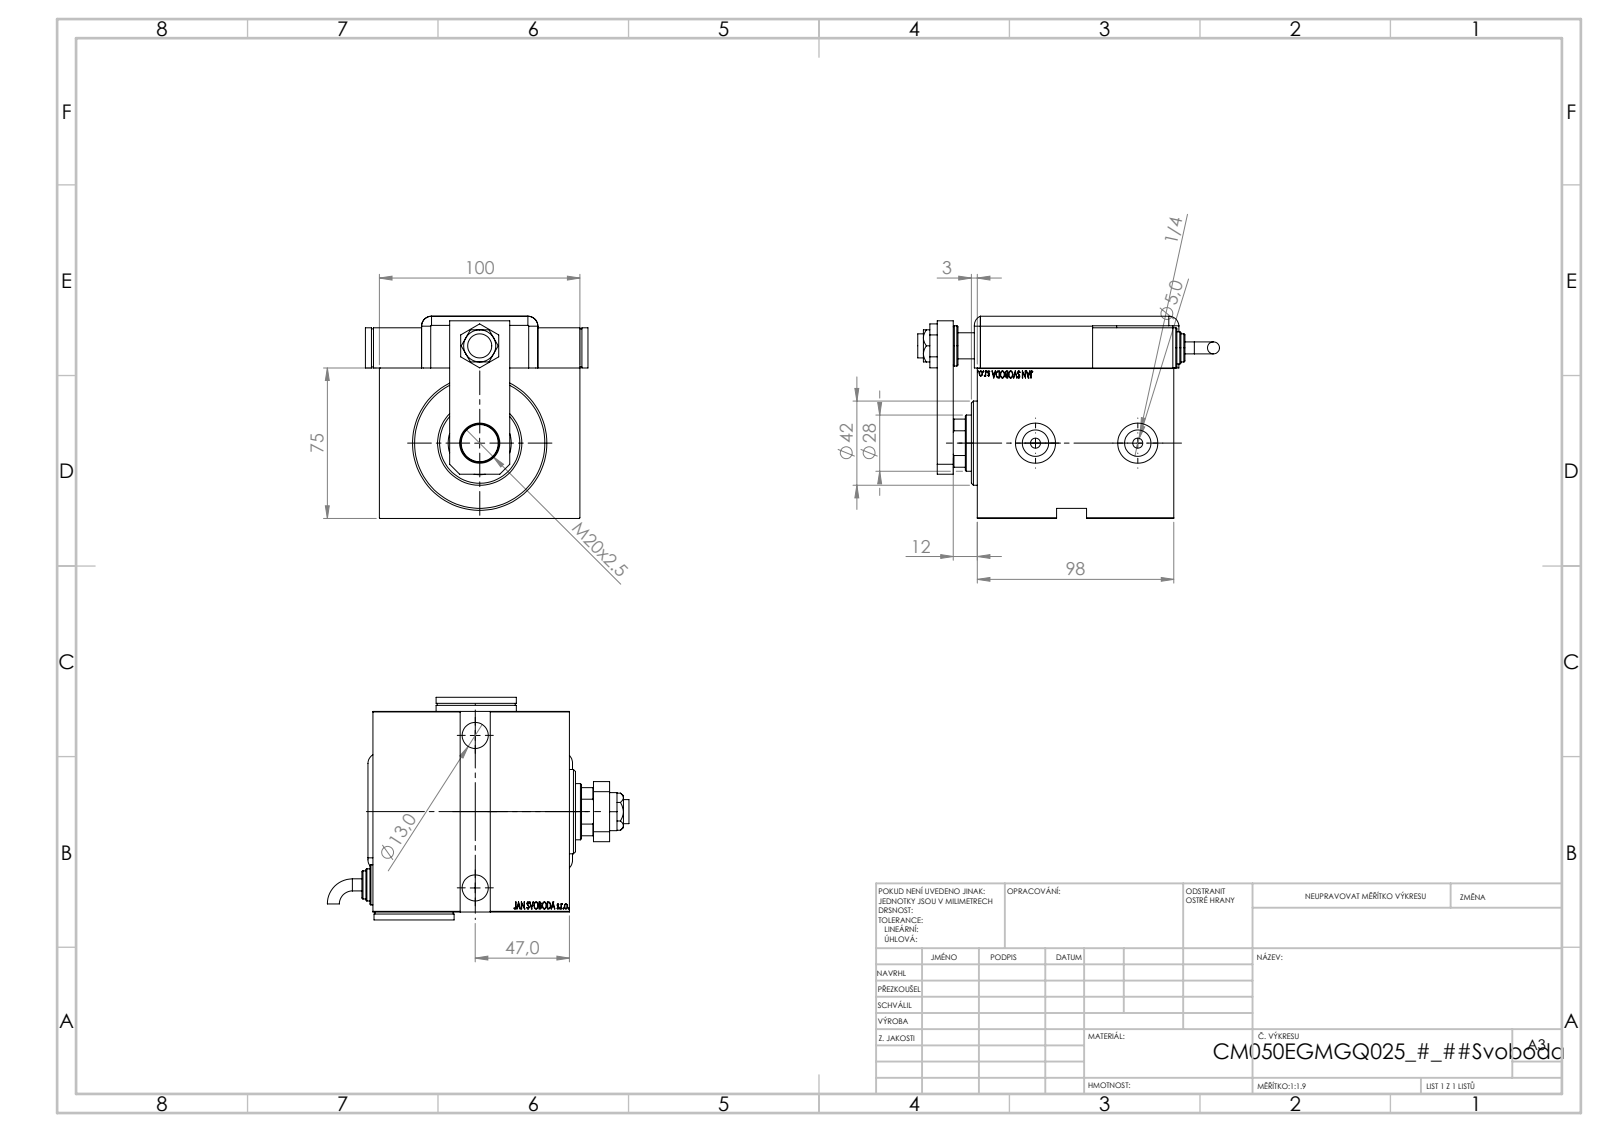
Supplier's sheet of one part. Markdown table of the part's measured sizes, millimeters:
| quantity | value |
| --- | --- |
| part name | NUT_D13; V450CM_E_VCP; V450CM_E_Body; NUT_D19 (+8 more) |
| STEP written by | SolidWorks 2019 (CONFIG_CONTROL_DESIGN) |
| units | millimeters |
| bodies | 13 solids, 1232 faces (616 planar, 99 cylindrical, 517 other) |
| overall size | 150.46 × 111 × 100.8 |
| volume | 815 841 mm³ |
| surface area | 152 555 mm² |
| round holes (diameter × count) | 13 × 3, 20 × 3, 4 × 2, 5 × 2, 8 × 2, 13.16 × 2, 19 × 2, 12 × 1, 14 × 1, 18.5 × 1, 28 × 1, 31.5 × 1 |
| round bosses / shafts (diameter × count) | 20 × 3, 16 × 2, 14 × 2, 6 × 2, 52 × 1, 42 × 1 |
| partial cylindrical surfaces (radius × count) | 5 × 9, 10 × 1, 13.5 × 1 |
| main face-to-face distances | 3, 75, 98, 100, 14, 20, 79, 84, 100.8, 25.8 |
| hole center spacings | 47.2, 61.22, 20, 48.5, 51, 76 |
